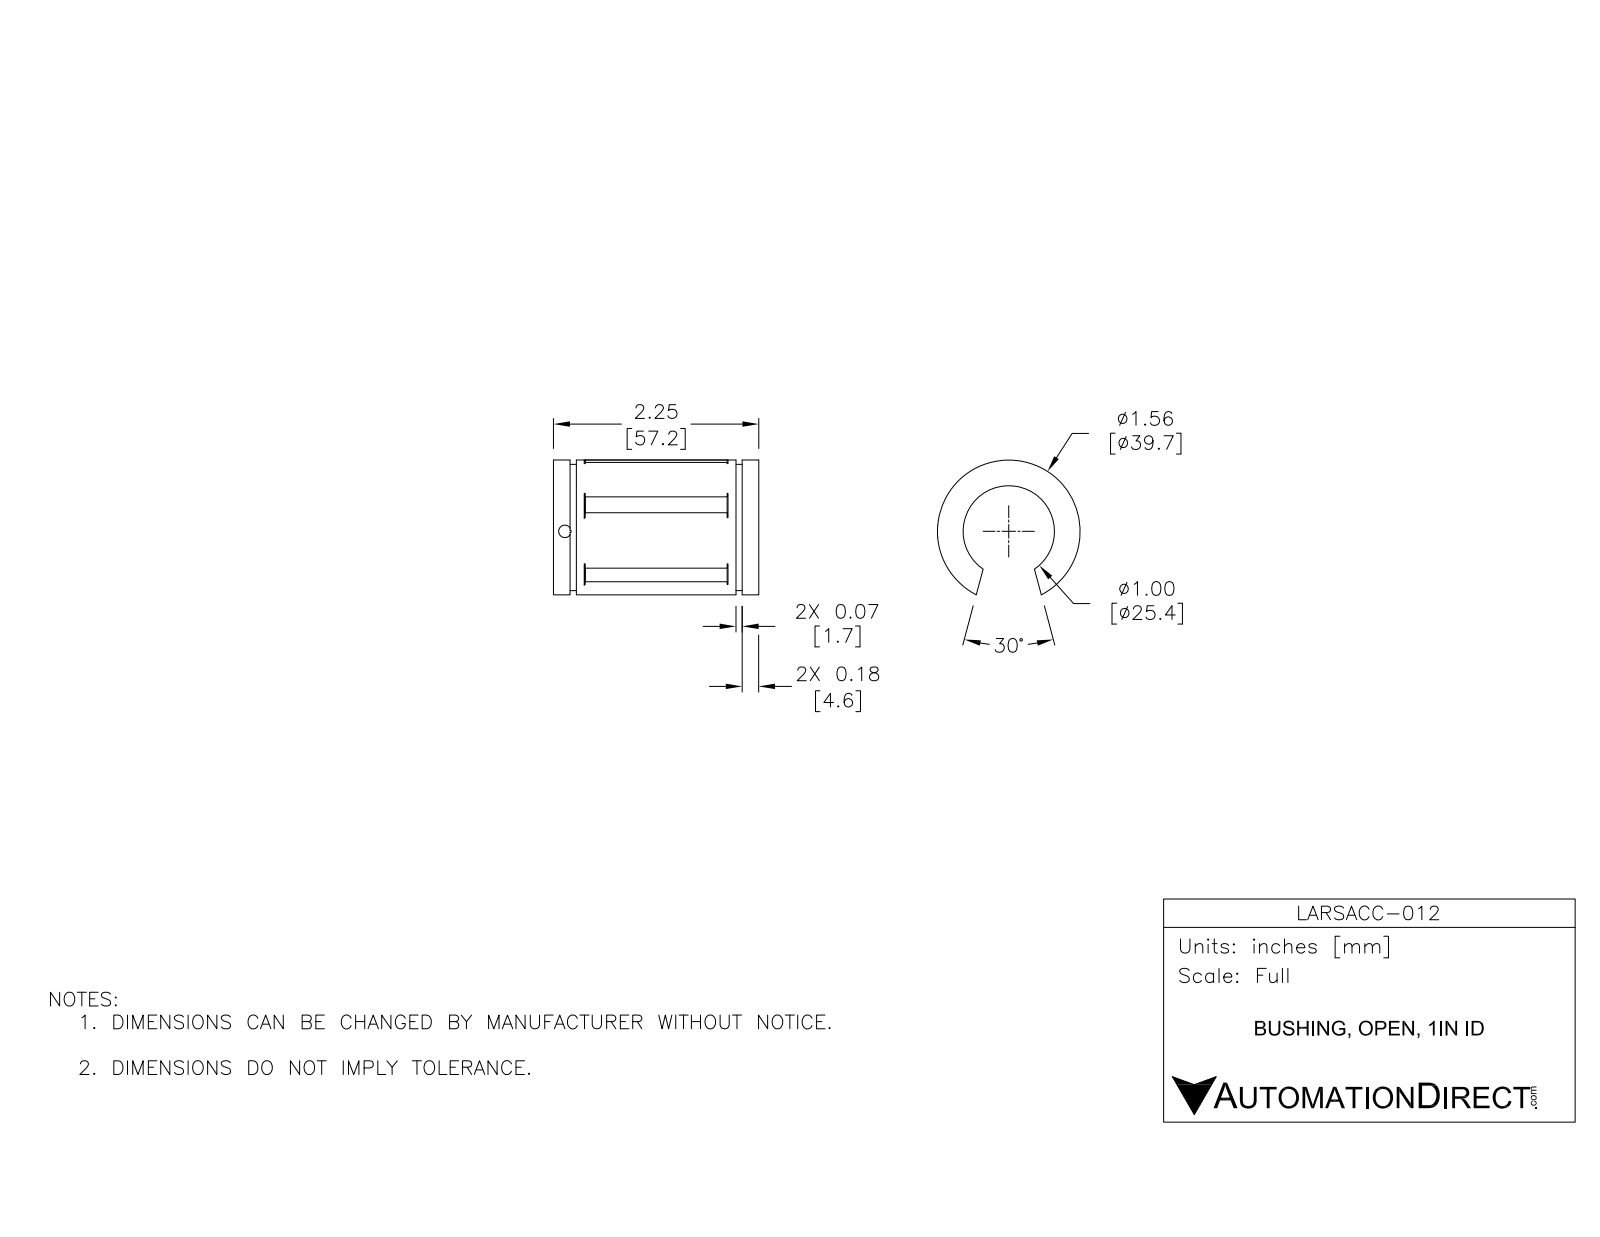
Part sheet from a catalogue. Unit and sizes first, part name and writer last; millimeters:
Units: millimetres
Overall size (bounding box): 57.2 × 39.7 × 37.5
Round holes (diameter × count): ⌀3.5 ×1, ⌀25.4 ×1
Round bosses / shafts (diameter × count): ⌀39.7 ×1, ⌀37.3 ×1
Partial cylindrical surfaces — rounded edges, fillets, slot ends (radius × count): R11.5 ×5, R14.5 ×5
Main face-to-face distances: 57.2, 6.4, 50.8, 4.6, 52.5, 46.2, 1.7, 44.5, 47.9, 39.8
Volume: 34 120 mm³ · Surface area: 12 350 mm²
Bodies: 1 solid, 67 faces (35 planar, 32 cylindrical, 0 other)
Part name (STEP PRODUCT): LARSACC-012
STEP written by: SolidWorks 2015 (AUTOMOTIVE_DESIGN)
